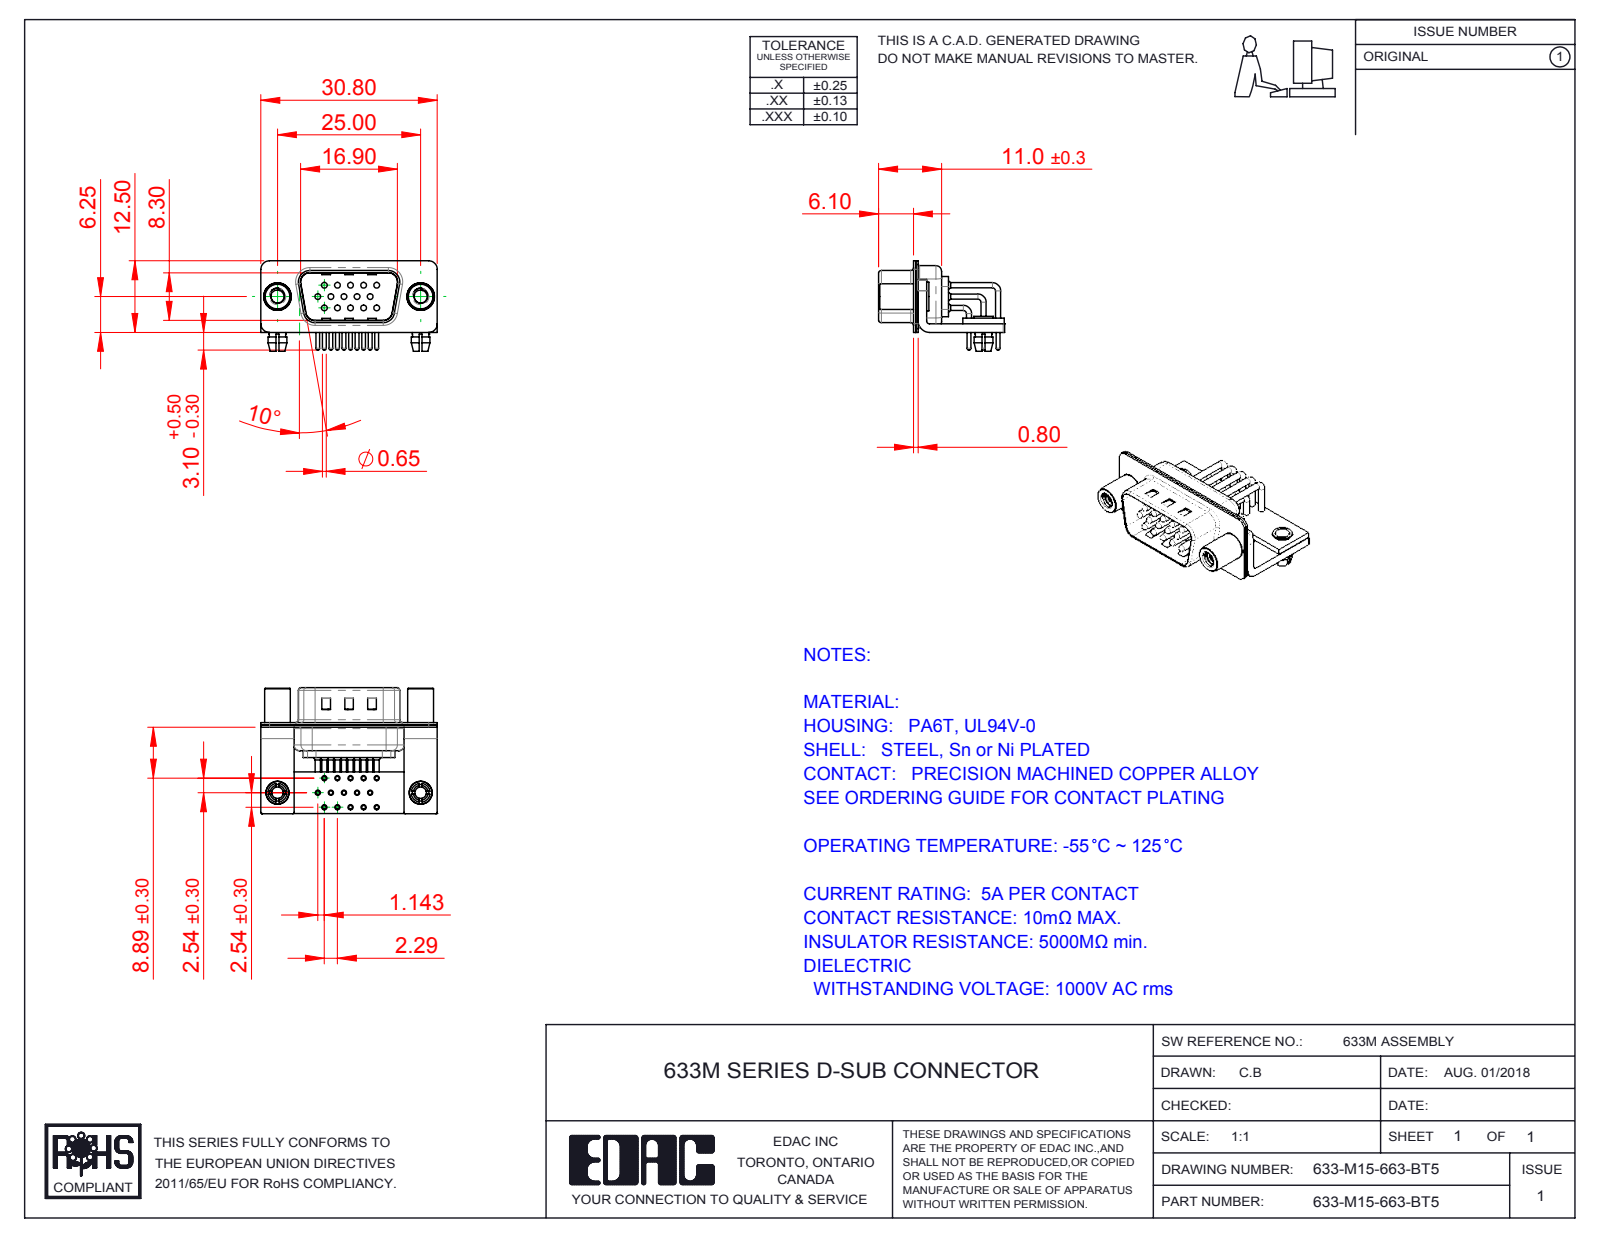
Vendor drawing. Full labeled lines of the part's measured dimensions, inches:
Part name (STEP PRODUCT): 633-M15-663-BT5; 633M Housing_15 Contacts; 633M Board Lock; 633M Contact Row 3 (+7 more)
STEP written by: SolidWorks 2016 (CONFIG_CONTROL_DESIGN)
Units: inches
Bodies: 25 solids, 2176 faces (1143 planar, 795 cylindrical, 238 other)
Overall size (bounding box): 1.213 × 0.866 × 0.622
Volume: 0.128 in³ · Surface area: 9.821 in²
Round holes (diameter × count): ⌀0.079 ×17, ⌀0.035 ×15, ⌀0.039 ×15, ⌀0.067 ×15, ⌀0.089 ×2, ⌀0.098 ×2, ⌀0.126 ×2, ⌀0.157 ×2, ⌀0.189 ×2
Round bosses / shafts (diameter × count): ⌀0.035 ×16, ⌀0.059 ×15, ⌀0.026 ×15, ⌀0.197 ×2, ⌀0.193 ×2, ⌀0.177 ×2, ⌀0.157 ×2, ⌀0.134 ×2
Partial cylindrical surfaces — rounded edges, fillets, slot ends (radius × count): R0.01 ×16, R0.059 ×16, R0.04 ×15, R0.079 ×13, R0.02 ×9, R0.063 ×8, R0.024 ×4, R0.026 ×4
Main face-to-face distances: 0.016, 0.059, 0.031, 0.039, 0.033, 0.075, 0.098, 0.049, 0.409, 0.376
Hole centre spacings: 0.09, 0.18, 0.09, 0.156, 0.109, 0.168, 0.238, 0.27
